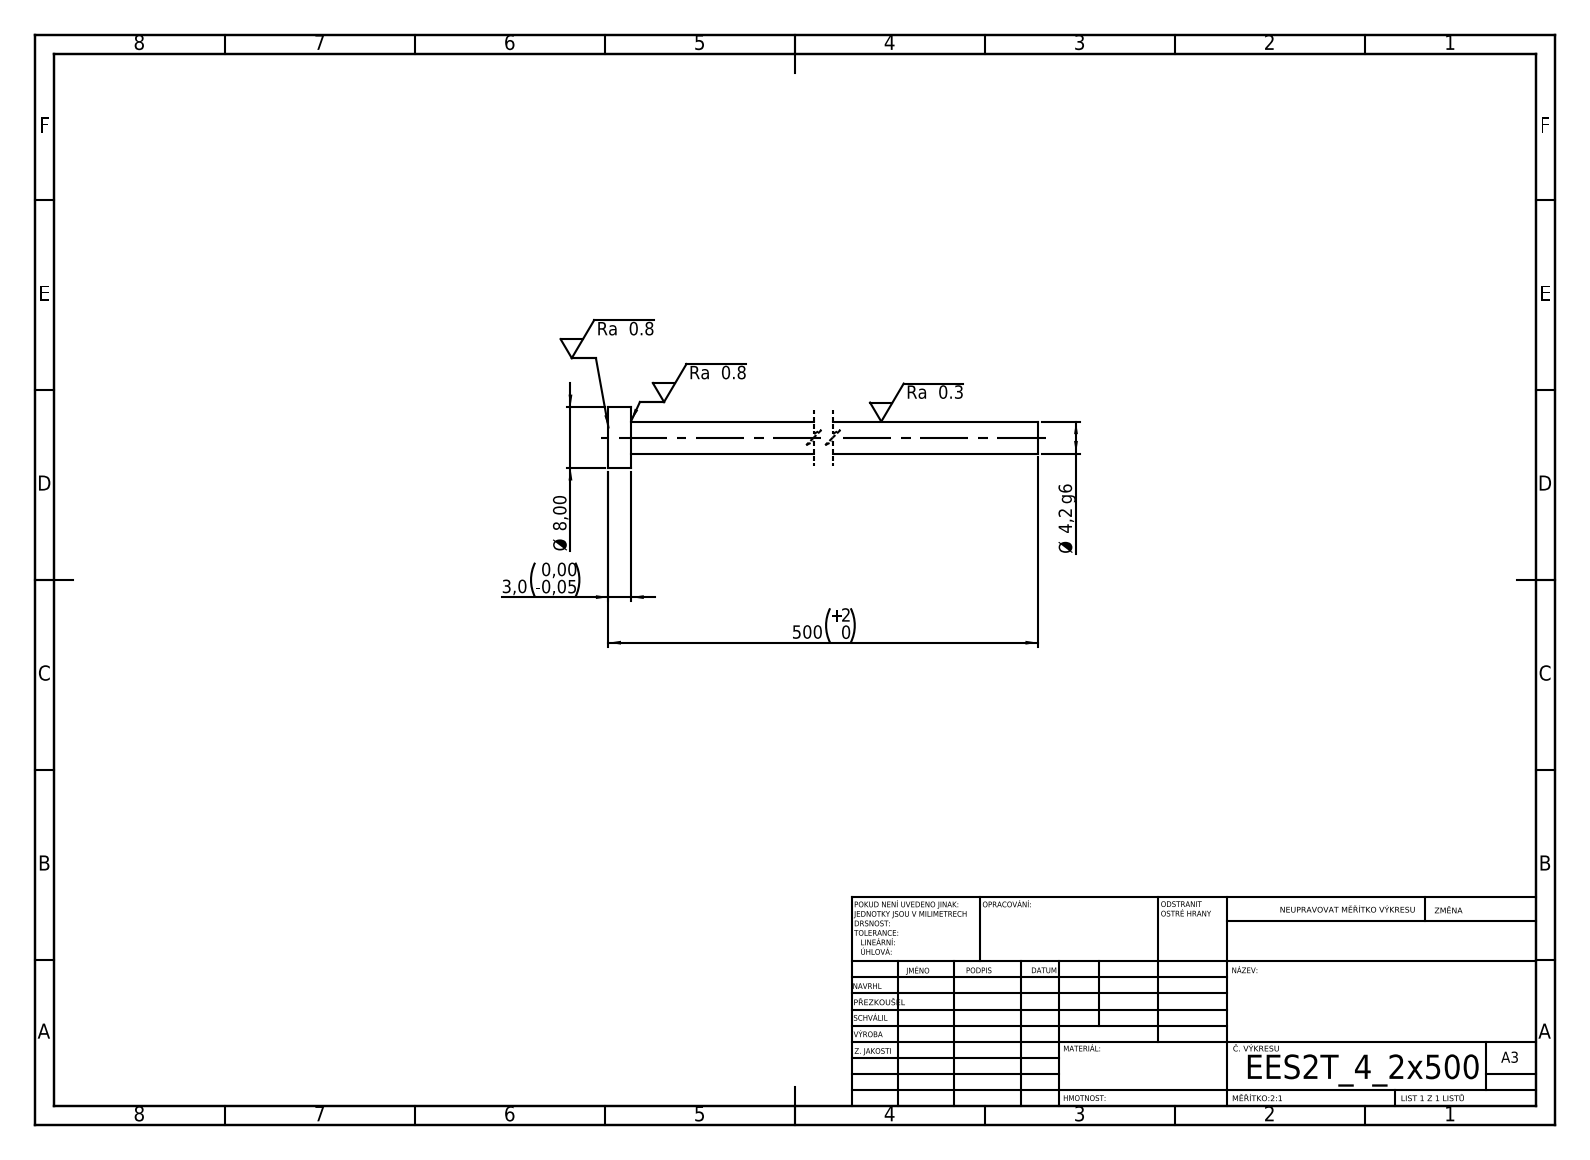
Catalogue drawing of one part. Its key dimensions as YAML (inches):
step_written_by: "SolidWorks 2019 (CONFIG_CONTROL_DESIGN)"
units: inches
bodies: {solids: 1, faces: 7, planar: 3, cylindrical: 4, other: 0}
overall_size: [19.685, 0.315, 0.315]
volume: 0.429
surface_area: 10.44
round_bosses_or_shafts:
  - {diameter: 0.315, count: 1}
  - {diameter: 0.165, count: 1}
face_to_face_distances: [0.118, 19.685, 19.567]
